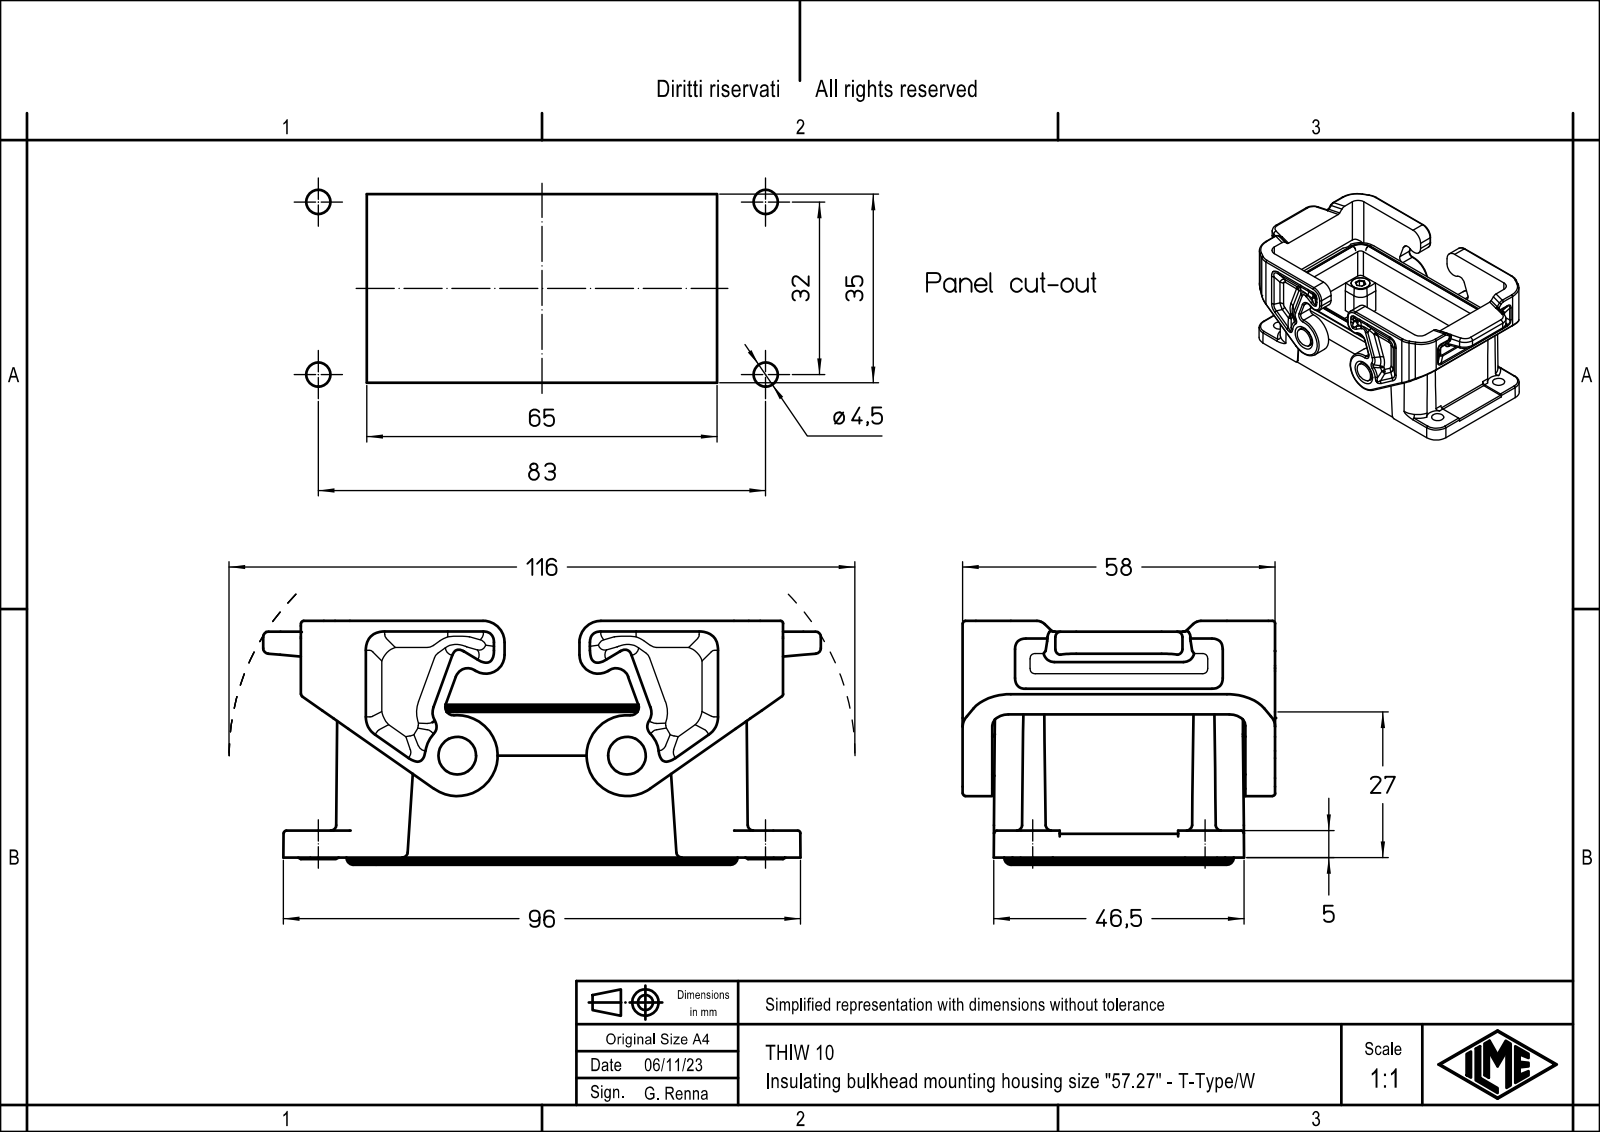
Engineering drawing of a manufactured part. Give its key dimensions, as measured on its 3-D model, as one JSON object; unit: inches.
{"part_name": "THIW 10", "step_written_by": "Creo Elements/Direct Modeling 20.1B 02-Apr-2019 (C) Parametric Technology GmbH (AUTOMOTIVE_DESIGN)", "units": "inches", "bodies": {"solids": 1, "faces": 681, "planar": 300, "cylindrical": 213, "other": 168}, "overall_size": [4.075, 2.283, 1.781], "volume_in3": 3.926, "surface_area_in2": 53.24, "round_holes": [[0.098, 4], [0.177, 4], [0.283, 2]], "round_bosses_or_shafts": [[0.189, 4], [0.276, 2]], "partial_cylinders_radius": [[0.039, 25], [0.051, 16], [0.079, 12], [0.118, 12], [0.217, 12], [0.059, 10], [0.197, 8], [0.236, 8]], "face_to_face_distances": [1.598, 0.217, 2.067, 1.85, 2.78, 0.079, 1.728, 2.283, 0.197, 3.13], "hole_center_spacings": [0.521, 1.269, 2.757, 2.991, 1.063, 1.26, 2.244, 2.483]}
